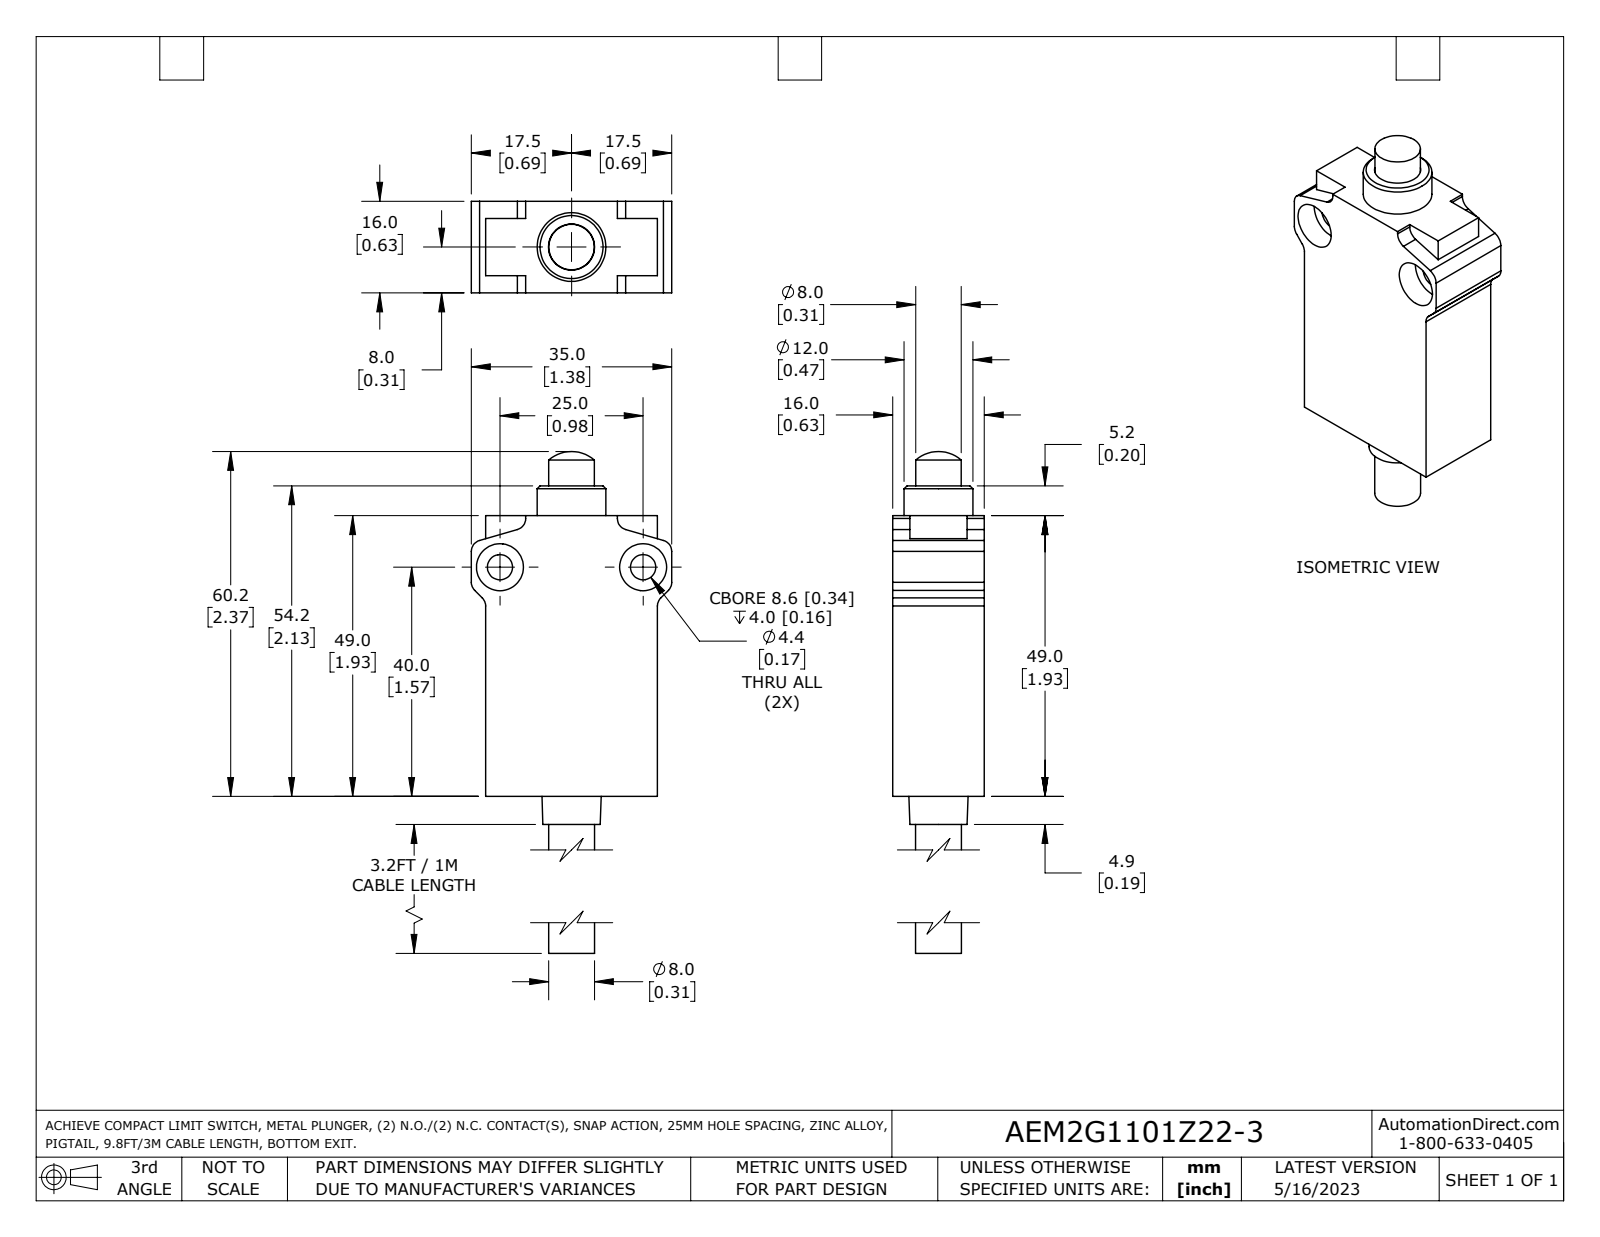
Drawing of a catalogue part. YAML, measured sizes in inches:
part_name: "AEM2G1101Z22-3"
step_written_by: "SolidWorks 2021 (AUTOMOTIVE_DESIGN)"
units: inches
bodies: {solids: 1, faces: 76, planar: 44, cylindrical: 25, other: 7}
overall_size: [2.957, 1.378, 0.63]
volume: 1.489
surface_area: 11.34
round_holes:
  - {diameter: 0.173, count: 2}
  - {diameter: 0.323, count: 2}
  - {diameter: 0.317, count: 1}
round_bosses_or_shafts:
  - {diameter: 0.472, count: 1}
  - {diameter: 0.315, count: 1}
  - {diameter: 0.313, count: 1}
partial_cylinders:
  - {radius: 0.079, count: 8}
  - {radius: 0.256, count: 1}
face_to_face_distances: [0.63, 1.181, 1.929, 0.157, 0.098, 1.28, 0.472, 0.354, 0.039, 1.378]
hole_center_spacings: [0.984]
